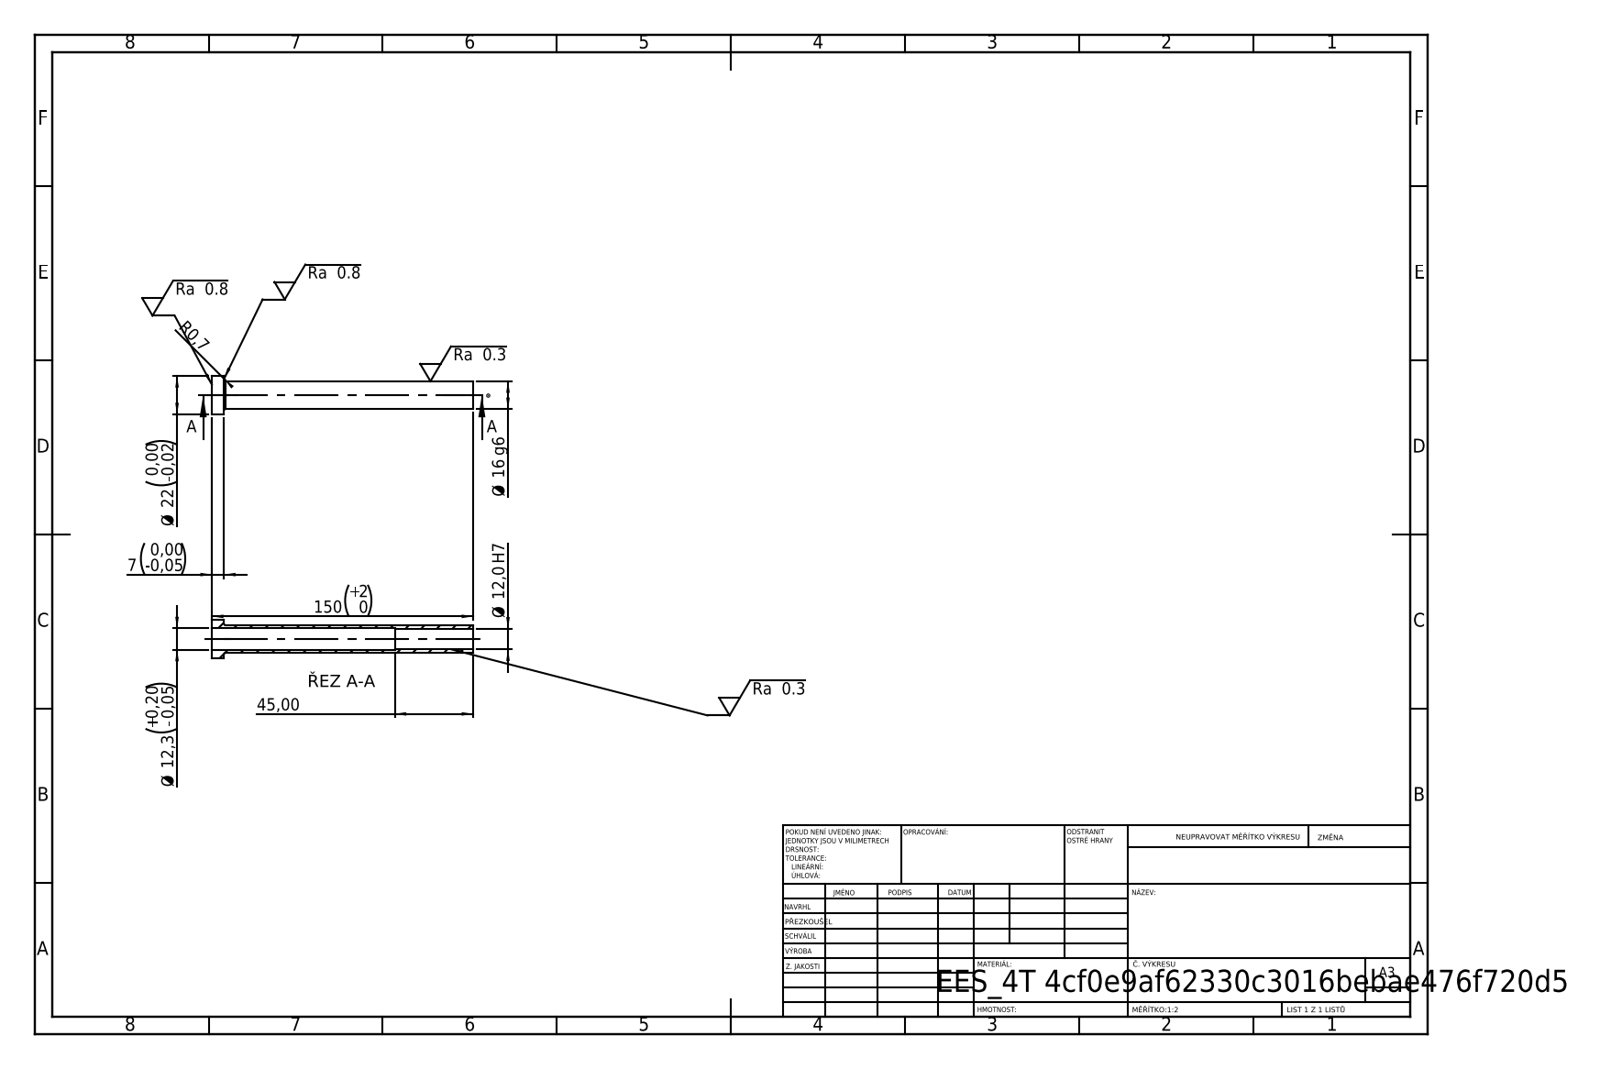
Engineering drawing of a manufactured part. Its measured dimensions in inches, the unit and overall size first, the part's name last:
Units: inches
Overall size (bounding box): 5.906 × 0.866 × 0.866
Round holes (diameter × count): ⌀0.472 ×1, ⌀0.484 ×1
Round bosses / shafts (diameter × count): ⌀0.866 ×1, ⌀0.63 ×1
Main face-to-face distances: 0.276, 5.906, 5.63, 4.134, 3.858, 1.772
Volume: 0.845 in³ · Surface area: 21.61 in²
Bodies: 1 solid, 14 faces (4 planar, 8 cylindrical, 2 other)
STEP written by: SolidWorks 2019 (CONFIG_CONTROL_DESIGN)
